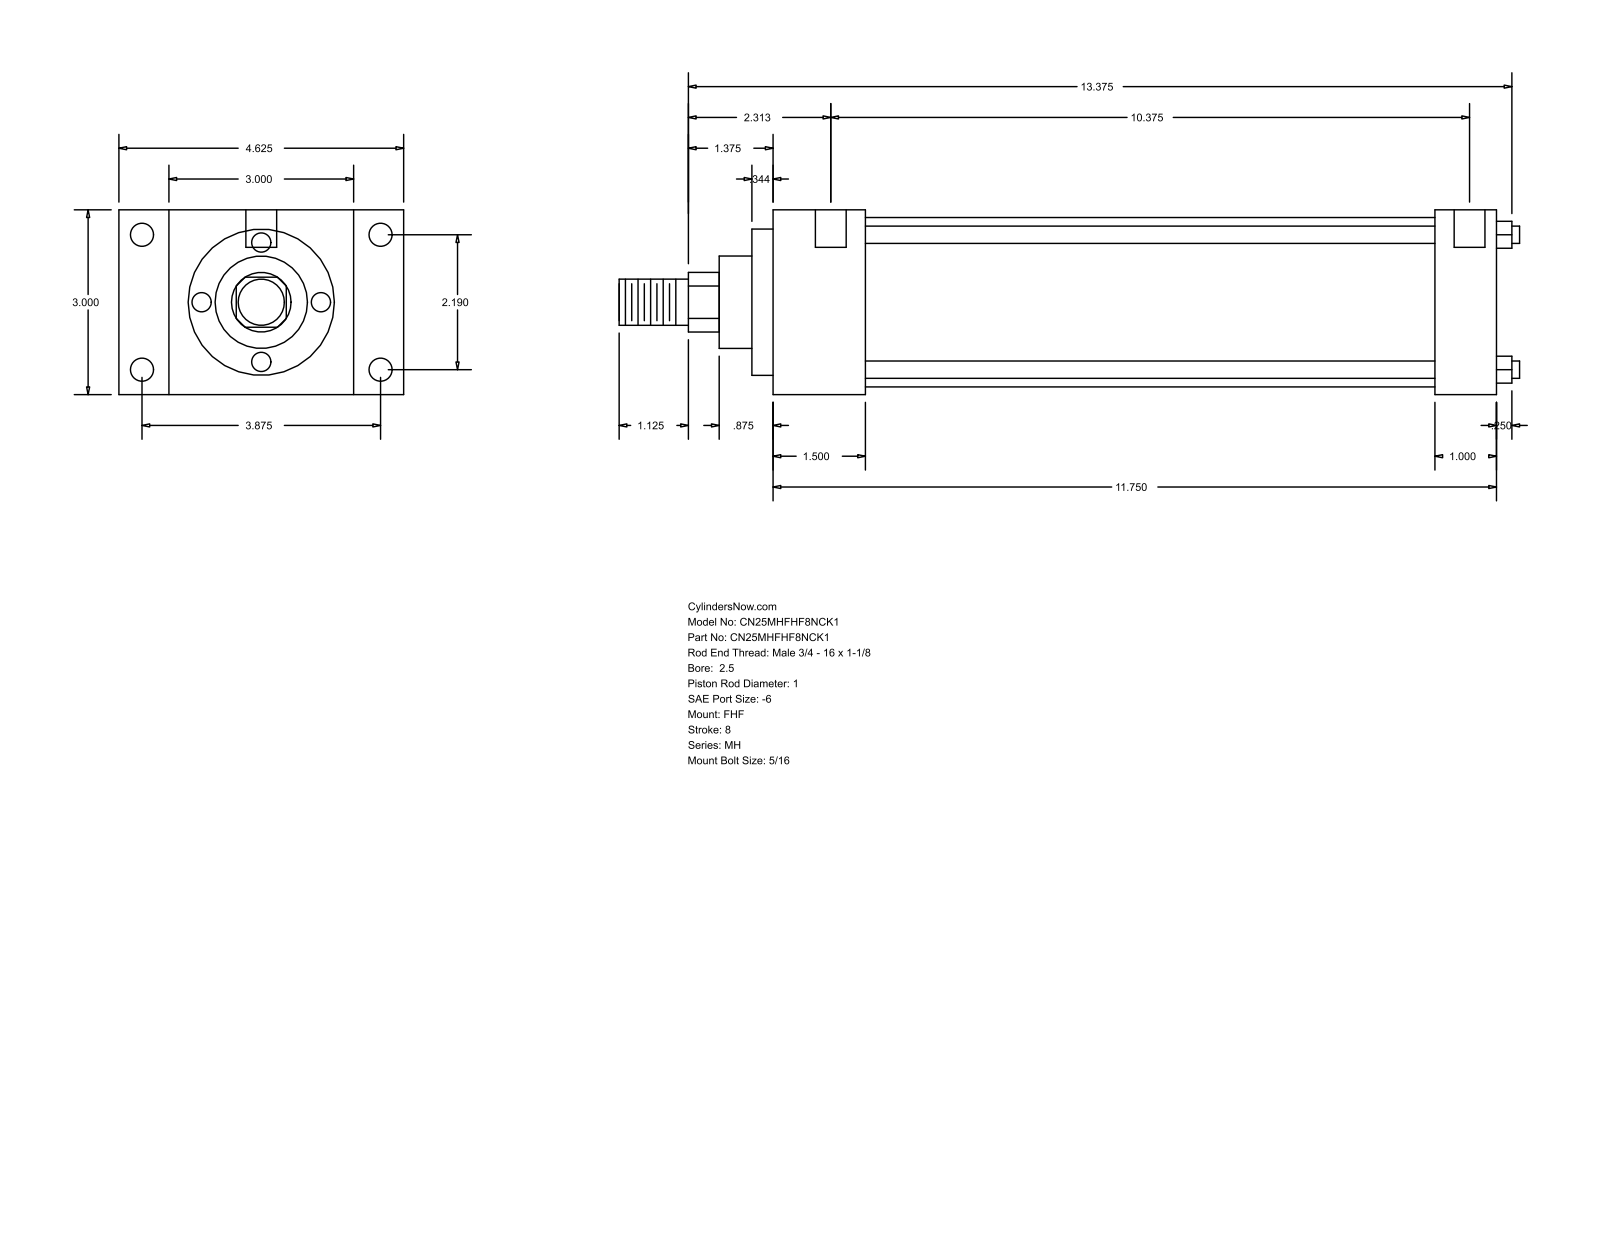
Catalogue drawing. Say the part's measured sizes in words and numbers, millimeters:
The part is named "MH_FHF__0250_1". Its 3-D file was written by "GSSL Pune (CONFIG_CONTROL_DESIGN)". It is 0 solids with 90 faces: 61 planar, 29 cylindrical and 0 other. Overall it measures 371.48 by 117.47 by 76.2 millimeters. Round holes: 4 of diameter 5.56, 4 of diameter 9.53, 2 of diameter 12.7. Round bosses or shafts: 4 of diameter 7.14, 1 of diameter 69.85, 1 of diameter 60.33, 1 of diameter 38.1, 1 of diameter 25.4, 1 of diameter 19.05. Partial cylindrical surfaces (rounded edges, fillets, slot ends): 1 of radius 12.29. The main face-to-face distances are 76.2, 298.46, 38.11, 260.35, 20.64, 96.84, 117.48, 273.06, 234.95, 25.4. The hole center spacings are 55.62, 98.42, 113.05, 271.46, 3.18, 4.76, 263.52, 266.7.
